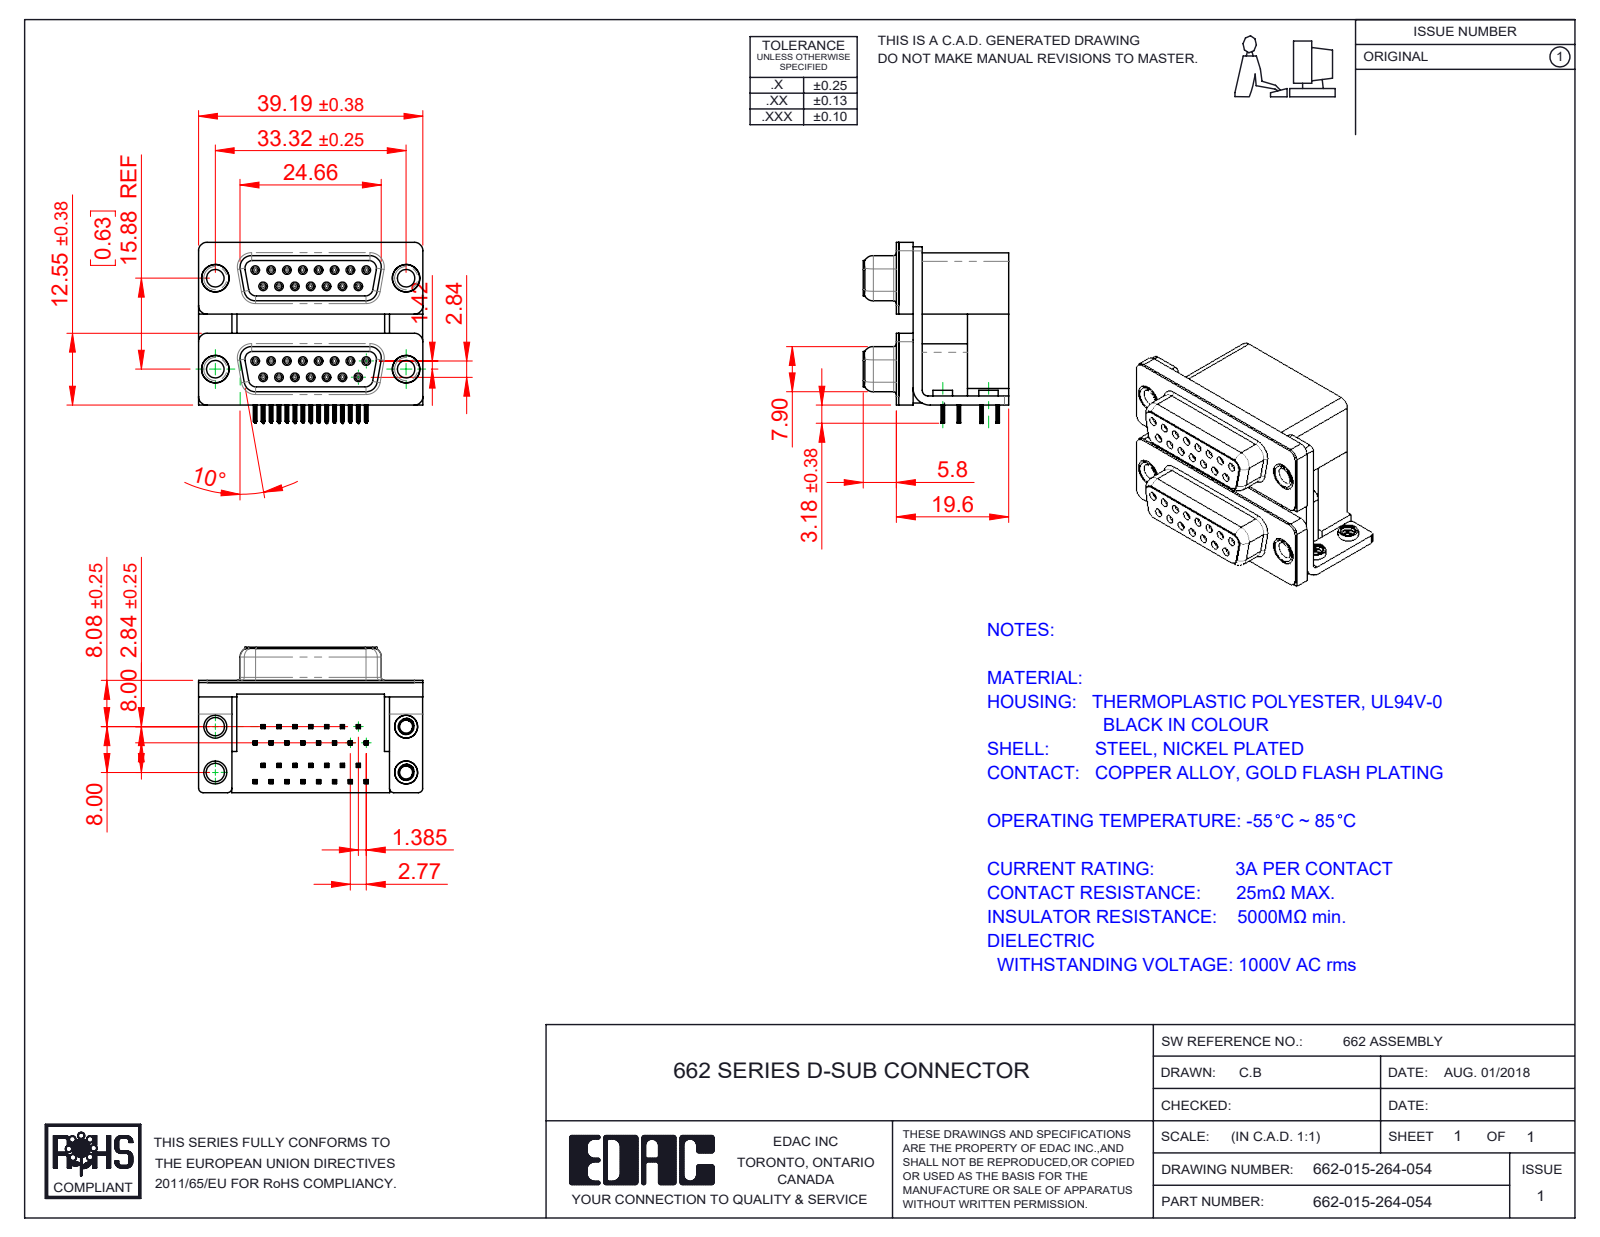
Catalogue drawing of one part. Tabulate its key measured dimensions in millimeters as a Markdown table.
| quantity | value |
| --- | --- |
| part name | 662 Housing Upper_15 Contacts L; 662 Contact Bottom Lower; 662 Mounting Bracket_ThruL; 662 Housing Spacer_15 Contacts L (+8 more) |
| STEP written by | SolidWorks 2020 (CONFIG_CONTROL_DESIGN) |
| units | millimeters |
| bodies | 45 solids, 4918 faces (2208 planar, 1214 cylindrical, 1496 other) |
| overall size | 39.19 × 31.61 × 25.4 |
| volume | 15 383 mm³ |
| surface area | 17 549 mm² |
| round holes (diameter × count) | 0.8 × 30, 0.9 × 30, 2.26 × 4, 2.75 × 4, 3.05 × 4, 3.2 × 4, 3.5 × 4, 4 × 4, 4.8 × 4, 5 × 4 |
| round bosses / shafts (diameter × count) | 1.2 × 30, 4.9 × 4, 4.75 × 4, 4 × 4, 3.85 × 4, 3.4 × 4 |
| partial cylindrical surfaces (radius × count) | 0.1 × 240, 0.15 × 120, 0.35 × 60, 0.34 × 30, 1.35 × 16, 1.5 × 15, 0.28 × 14, 0.5 × 8 |
| main face-to-face distances | 0.4, 19.2, 16.7, 2.5, 10.7, 2.9, 15.88, 7.2, 9.5, 12 |
| hole center spacings | 3.16, 16.12, 2.77, 16.82, 5.54, 8.31, 15.88, 17.92 |
